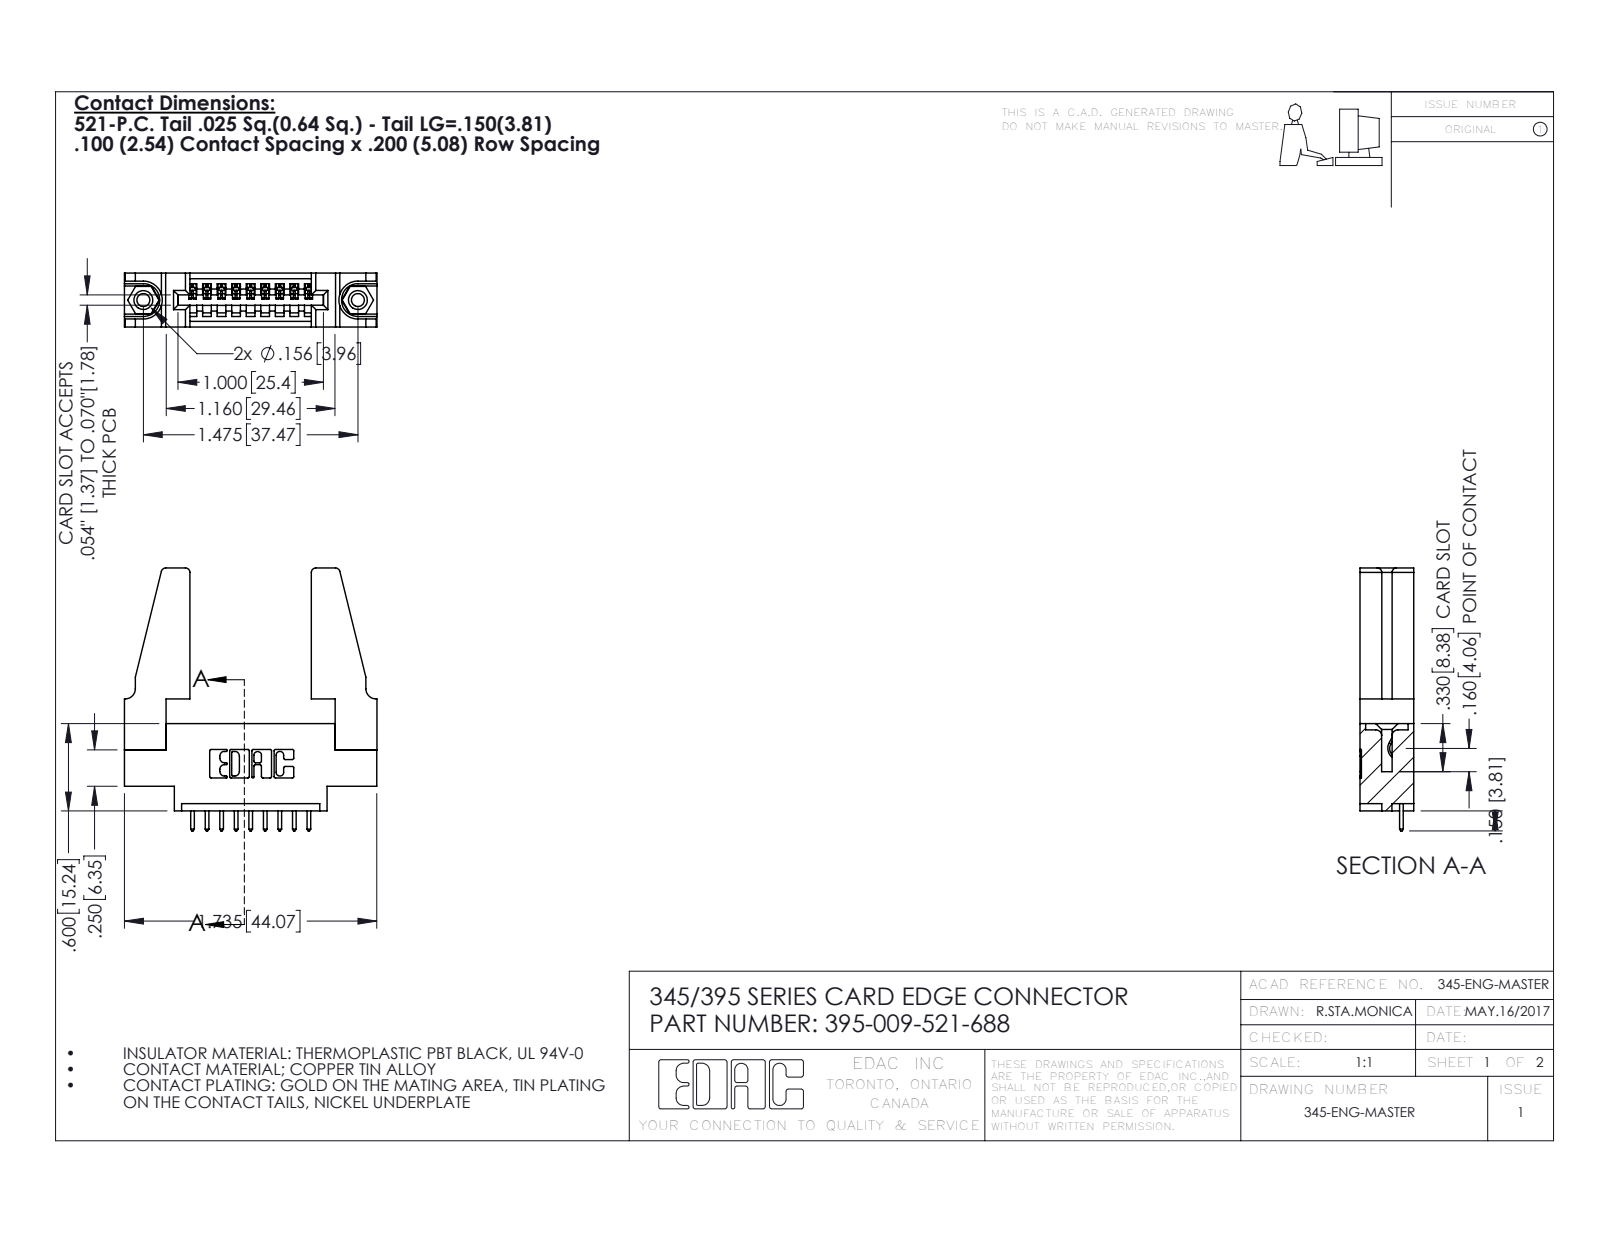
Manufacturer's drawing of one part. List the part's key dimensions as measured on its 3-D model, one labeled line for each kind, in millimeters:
Part name (STEP PRODUCT): 395-009-521-688; 345-250-001_345-250-001-102; 345 Part_0.170 Offset - 0.156 Dia-TH; 345-292-001_345-293-121 (+1 more)
STEP written by: SolidWorks 2016 (CONFIG_CONTROL_DESIGN)
Units: millimetres
Bodies: 14 solids, 776 faces (516 planar, 244 cylindrical, 16 other)
Overall size (bounding box): 45.9 × 44.1 × 9.4
Volume: 7 030 mm³ · Surface area: 7 729 mm²
Round holes (diameter × count): ⌀2.3 ×2, ⌀3.2 ×2, ⌀4 ×2, ⌀1.6 ×1
Round bosses / shafts (diameter × count): ⌀3.9 ×2
Partial cylindrical surfaces — rounded edges, fillets, slot ends (radius × count): R0.3 ×22, R0.2 ×18, R0.3 ×18, R0.8 ×8, R0.2 ×6, R0.8 ×6, R0.7 ×3, R0.8 ×2
Main face-to-face distances: 9.4, 1.8, 7.6, 2.5, 6.9, 0.6, 5.1, 3.8, 3.8, 5.7
Hole centre spacings: 6.9, 31.6, 37.5
